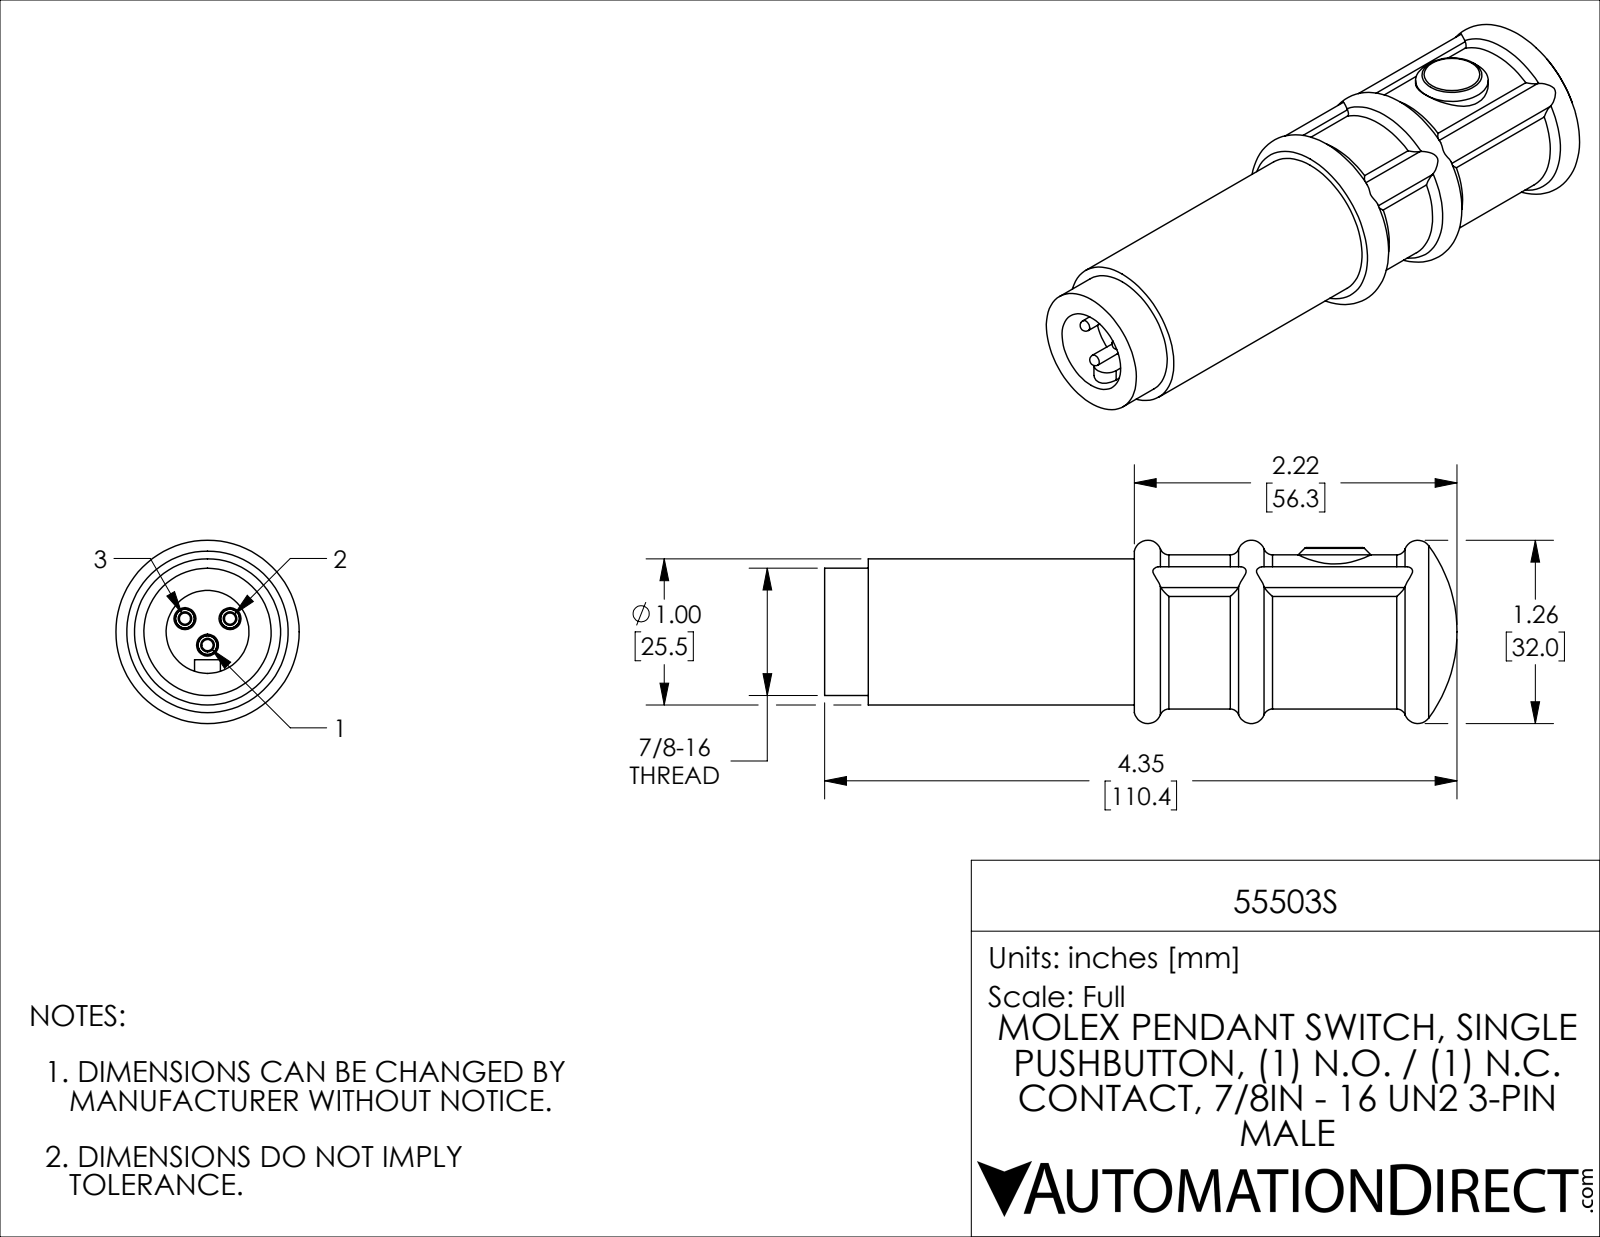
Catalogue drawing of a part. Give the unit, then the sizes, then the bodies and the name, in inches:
Units: inches
Overall size (bounding box): 4.348 × 1.26 × 1.26
Round holes (diameter × count): ⌀0.57 ×1
Round bosses / shafts (diameter × count): ⌀0.077 ×3, ⌀1.059 ×1, ⌀1.005 ×1, ⌀0.875 ×1, ⌀0.5 ×1
Partial cylindrical surfaces — rounded edges, fillets, slot ends (radius × count): R0.062 ×4, R0.094 ×3, R0.089 ×1, R0.529 ×1
Main face-to-face distances: 0.333, 0.3, 0.033, 2.13, 1.83, 1.797, 0.771, 0.178, 0.243, 0.057
Volume: 3.661 in³ · Surface area: 18.13 in²
Bodies: 4 solids, 99 faces (14 planar, 40 cylindrical, 45 other)
Part name (STEP PRODUCT): 55503S
STEP written by: SolidWorks 2021 (CONFIG_CONTROL_DESIGN)
